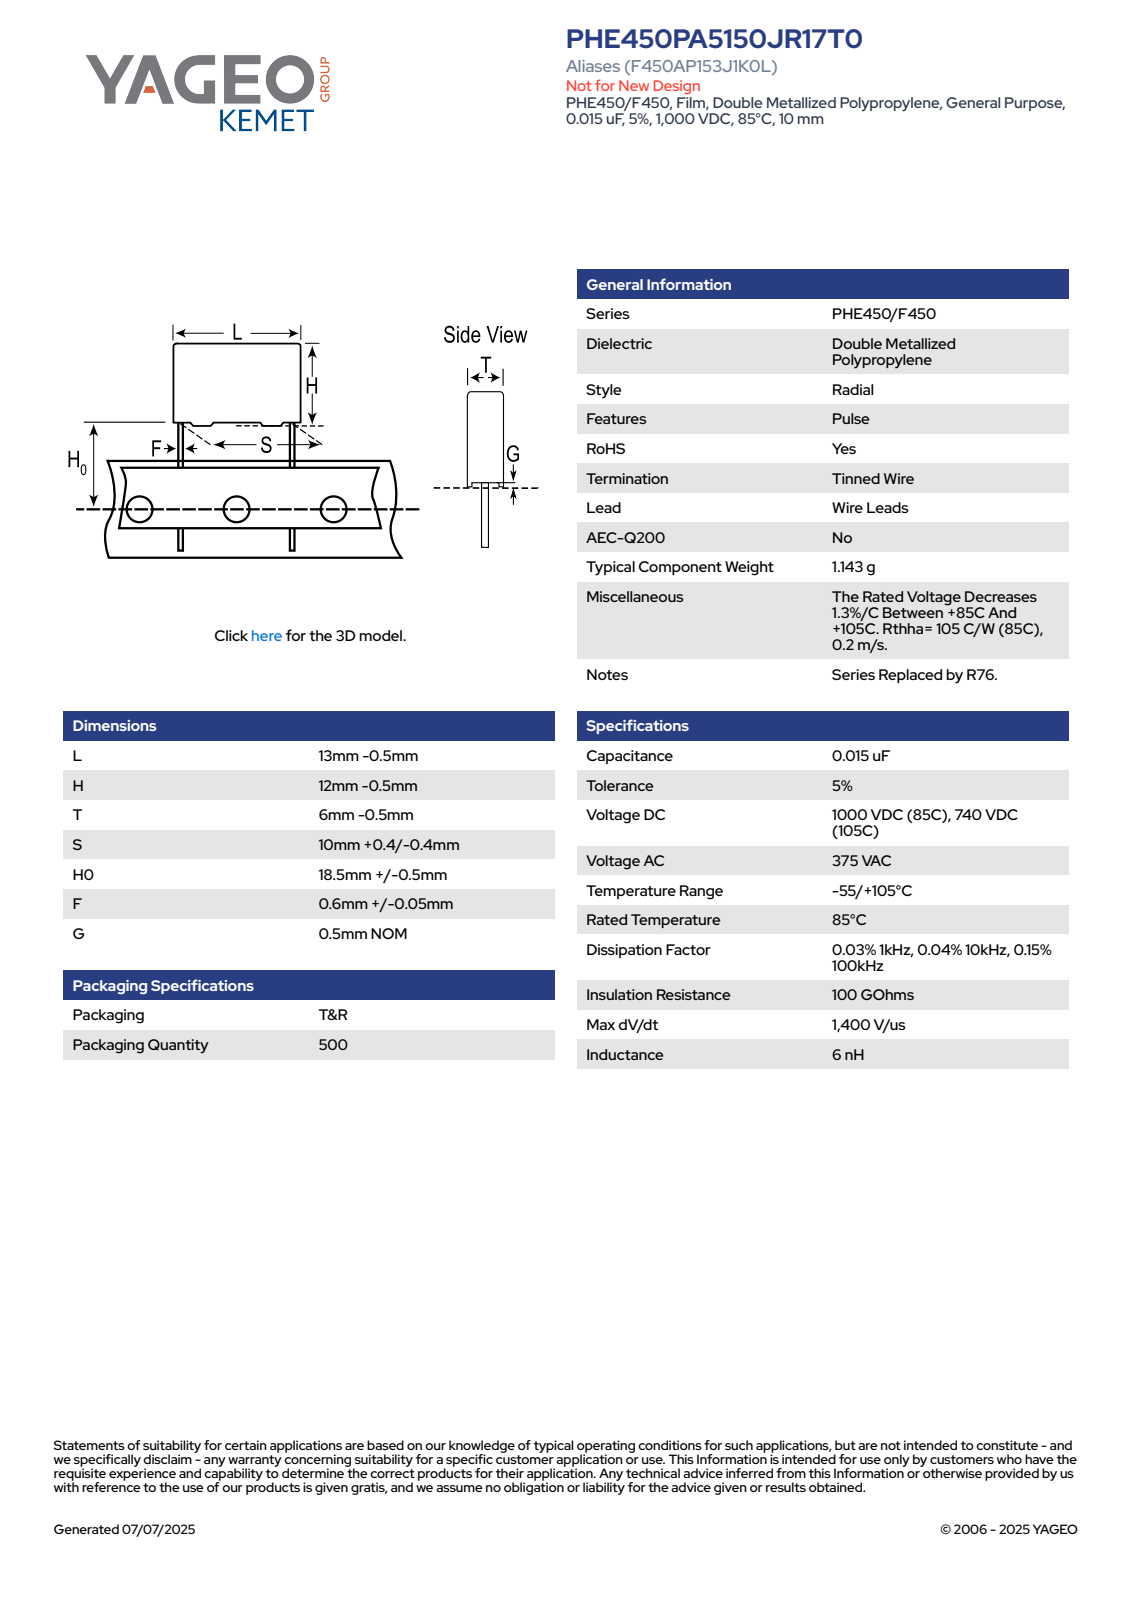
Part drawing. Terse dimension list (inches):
name: CFR_RBG_13X12X6_L12.5H11.5T5.5S10H019F0.65G0.5
written by: SolidWorks 2014 (AUTOMOTIVE_DESIGN)
unit: in
bodies: 4 solids, 89 faces (81 planar, 8 cylindrical, 0 other)
size: 1.201 × 0.492 × 0.217
volume: 0.047 in³; area: 0.978 in²
bosses: 2× ⌀0.026
rounds: 4× R0.02
face distances: 0.217, 0.492, 0.433, 0.012, 0.204, 0.02, 0.453, 0.192, 0.748, 0.768
